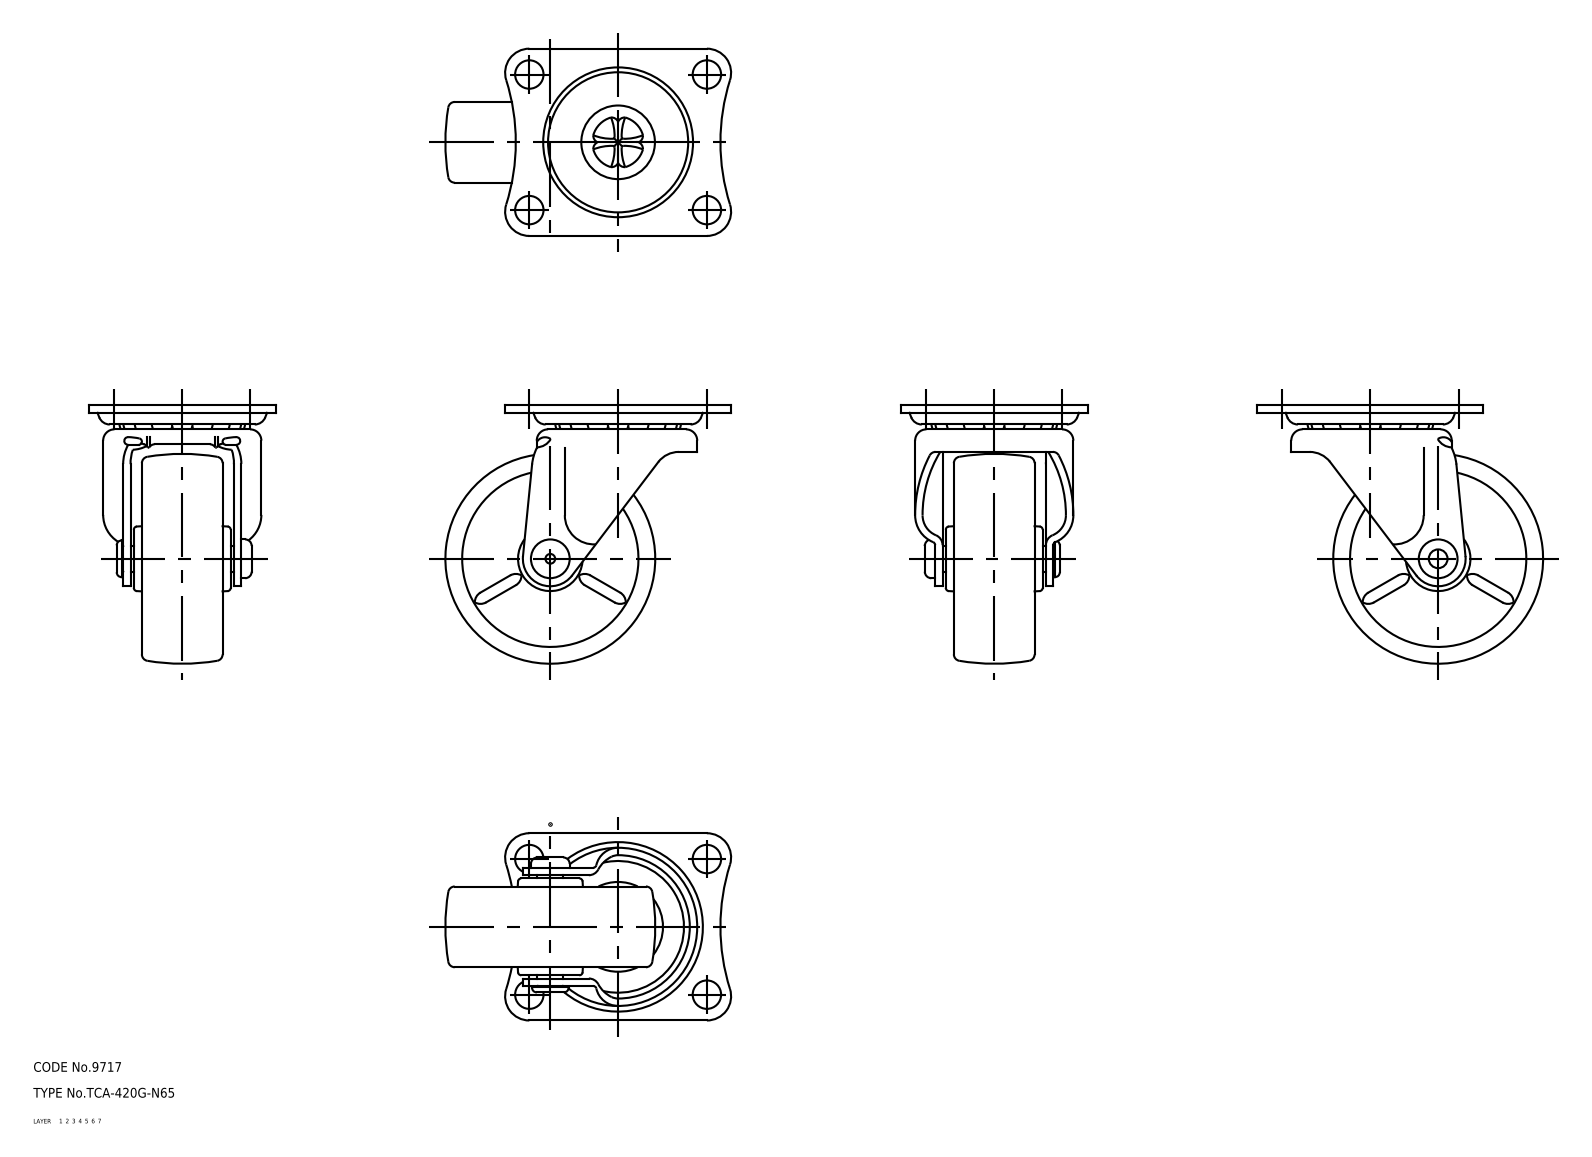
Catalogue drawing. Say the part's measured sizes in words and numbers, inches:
The part is named "wheel; mounting plate; main shaft; axle (+1 more)". Its 3-D file was written by "CADfix (AUTOMOTIVE_DESIGN)". It is 5 solids with 375 faces: 0 planar, 0 cylindrical and 375 other. Overall it measures 3.484 by 3.15 by 2.283 inches. Its volume is 5.366 cubic inches and its surface area 59 square inches.
